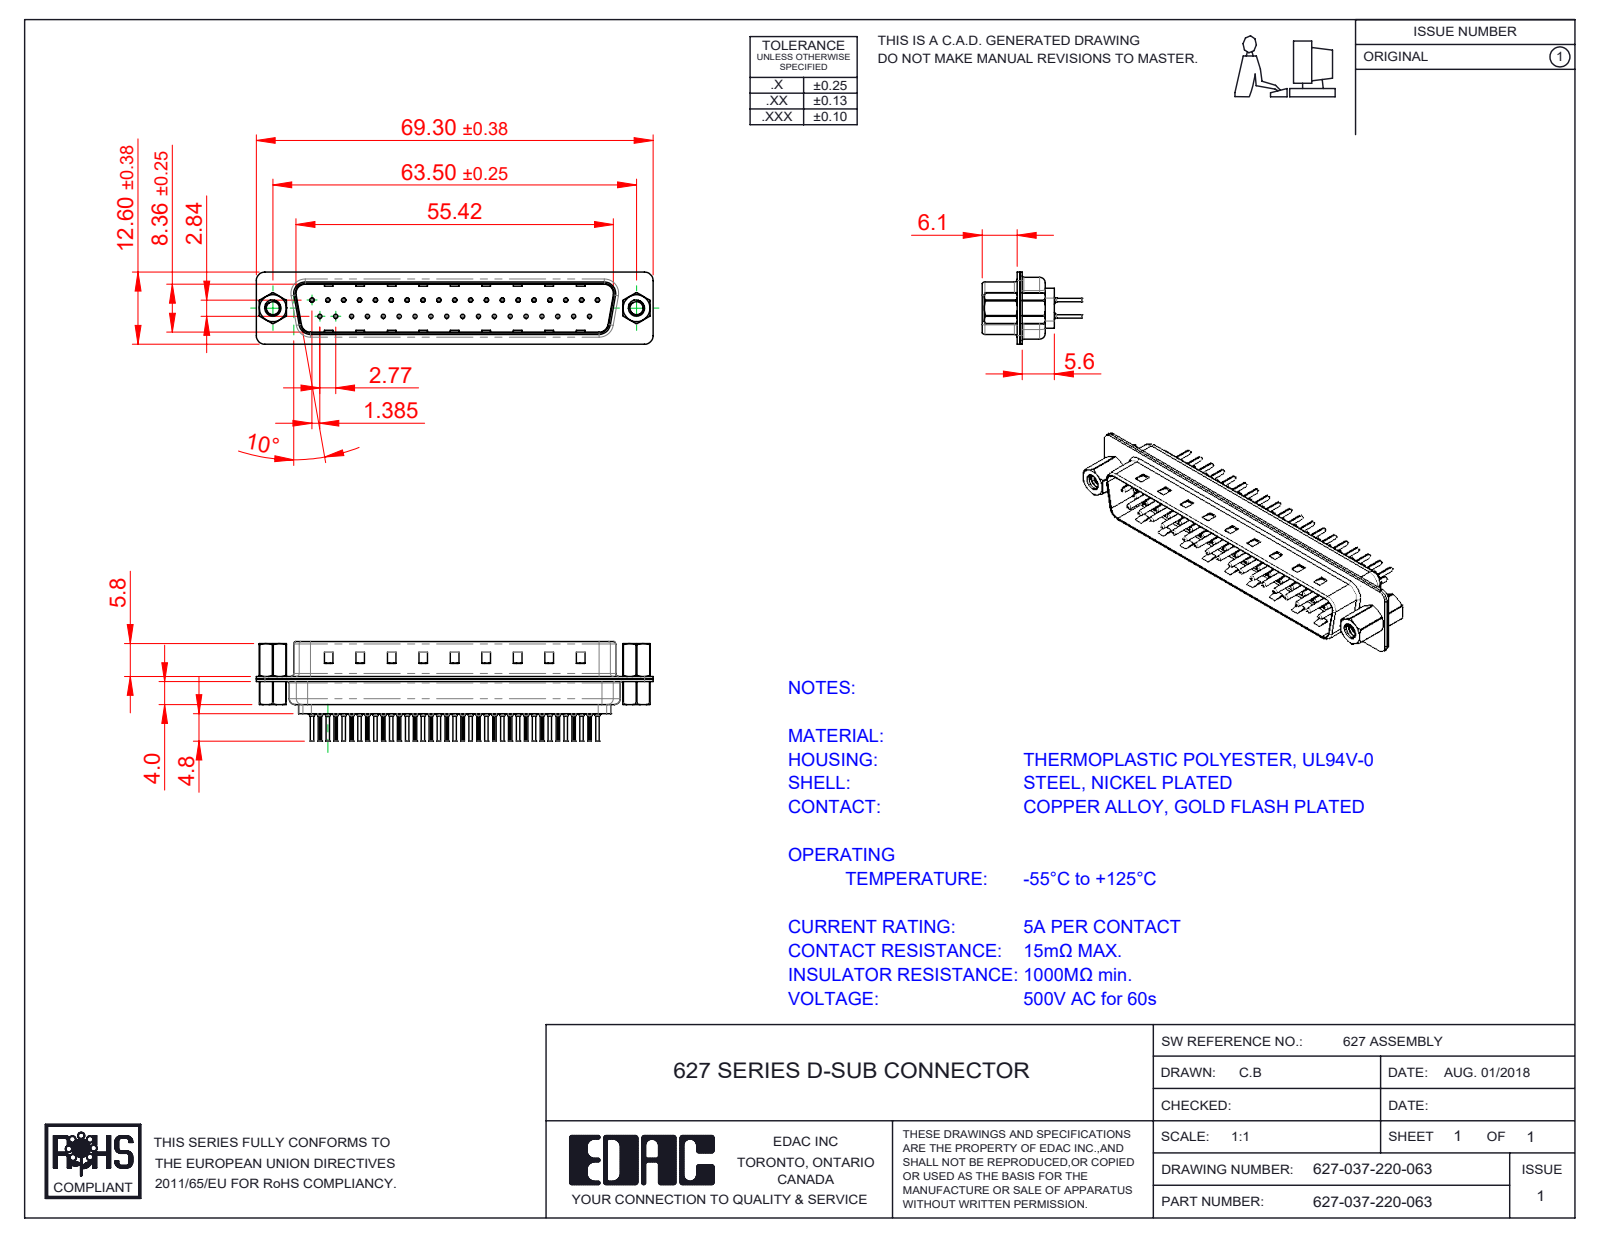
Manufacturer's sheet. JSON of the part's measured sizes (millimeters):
{"part_name": "627 4-40 Hex Standoff; 627 Housing_37 LP; 627-037-220-063; 627 Contact Row 2_20L (+4 more)", "step_written_by": "SolidWorks 2020 (CONFIG_CONTROL_DESIGN)", "units": "millimeters", "bodies": {"solids": 44, "faces": 4160, "planar": 1113, "cylindrical": 1580, "other": 1467}, "overall_size": [69.3, 17.3, 12.6], "volume_mm3": 3909, "surface_area_mm2": 11153, "round_holes": [[0.2, 37], [0.35, 37], [1.1, 37], [1.6, 37], [2.26, 2], [2.29, 2], [4, 2], [4.8, 2]], "round_bosses_or_shafts": [[2, 37], [1.5, 37], [0.75, 37], [0.6, 37], [5, 2], [4.9, 2], [2.79, 2]], "partial_cylinders_radius": [[0.1, 74], [1.5, 16], [2, 12], [0.5, 8], [1.6, 8], [0.25, 4], [0.6, 4], [0.65, 4]], "face_to_face_distances": [0.4, 0.82, 9.58, 0.45, 8.76, 1.5, 0.9, 1.4, 6.05, 6.5], "hole_center_spacings": [3.16, 2.77, 5.54, 8.31, 5.04, 10.1, 11.08, 12.78]}
